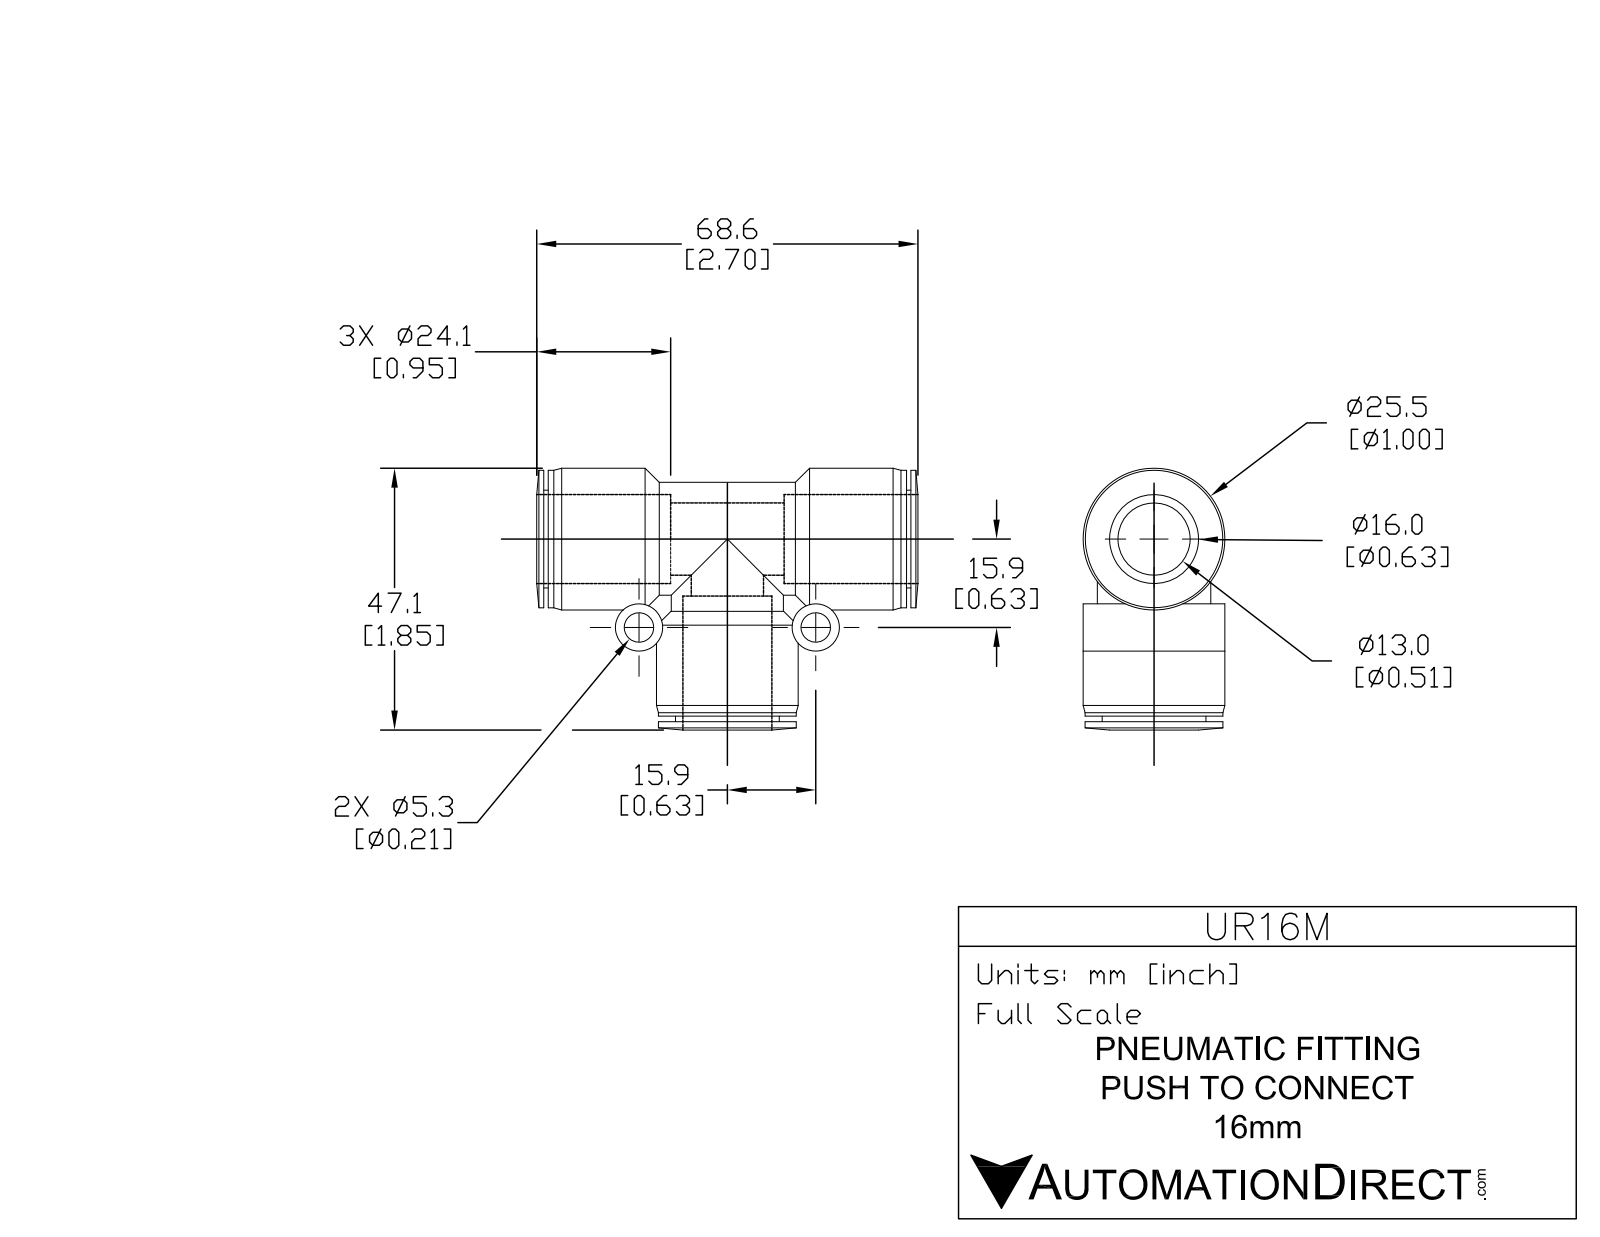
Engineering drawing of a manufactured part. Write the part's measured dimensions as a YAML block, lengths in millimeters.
part_name: "UT16M"
step_written_by: "SolidWorks 2015 (CONFIG_CONTROL_DESIGN)"
units: millimeters
bodies: {solids: 1, faces: 91, planar: 19, cylindrical: 51, other: 21}
overall_size: [68.6, 47.1, 25.5]
volume: 24916
surface_area: 15791
round_holes:
  - {diameter: 5.3, count: 2}
  - {diameter: 13, count: 2}
  - {diameter: 16, count: 2}
round_bosses_or_shafts:
  - {diameter: 25.5, count: 2}
  - {diameter: 20.4, count: 2}
  - {diameter: 8.5, count: 2}
  - {diameter: 24.8, count: 1}
  - {diameter: 24.74, count: 1}
  - {diameter: 18.68, count: 1}
  - {diameter: 17.58, count: 1}
face_to_face_distances: [0.8, 65.26, 66.06, 64.46, 1, 22.83, 43.23, 22.03, 42.43, 25.5]
hole_center_spacings: [31.8]
